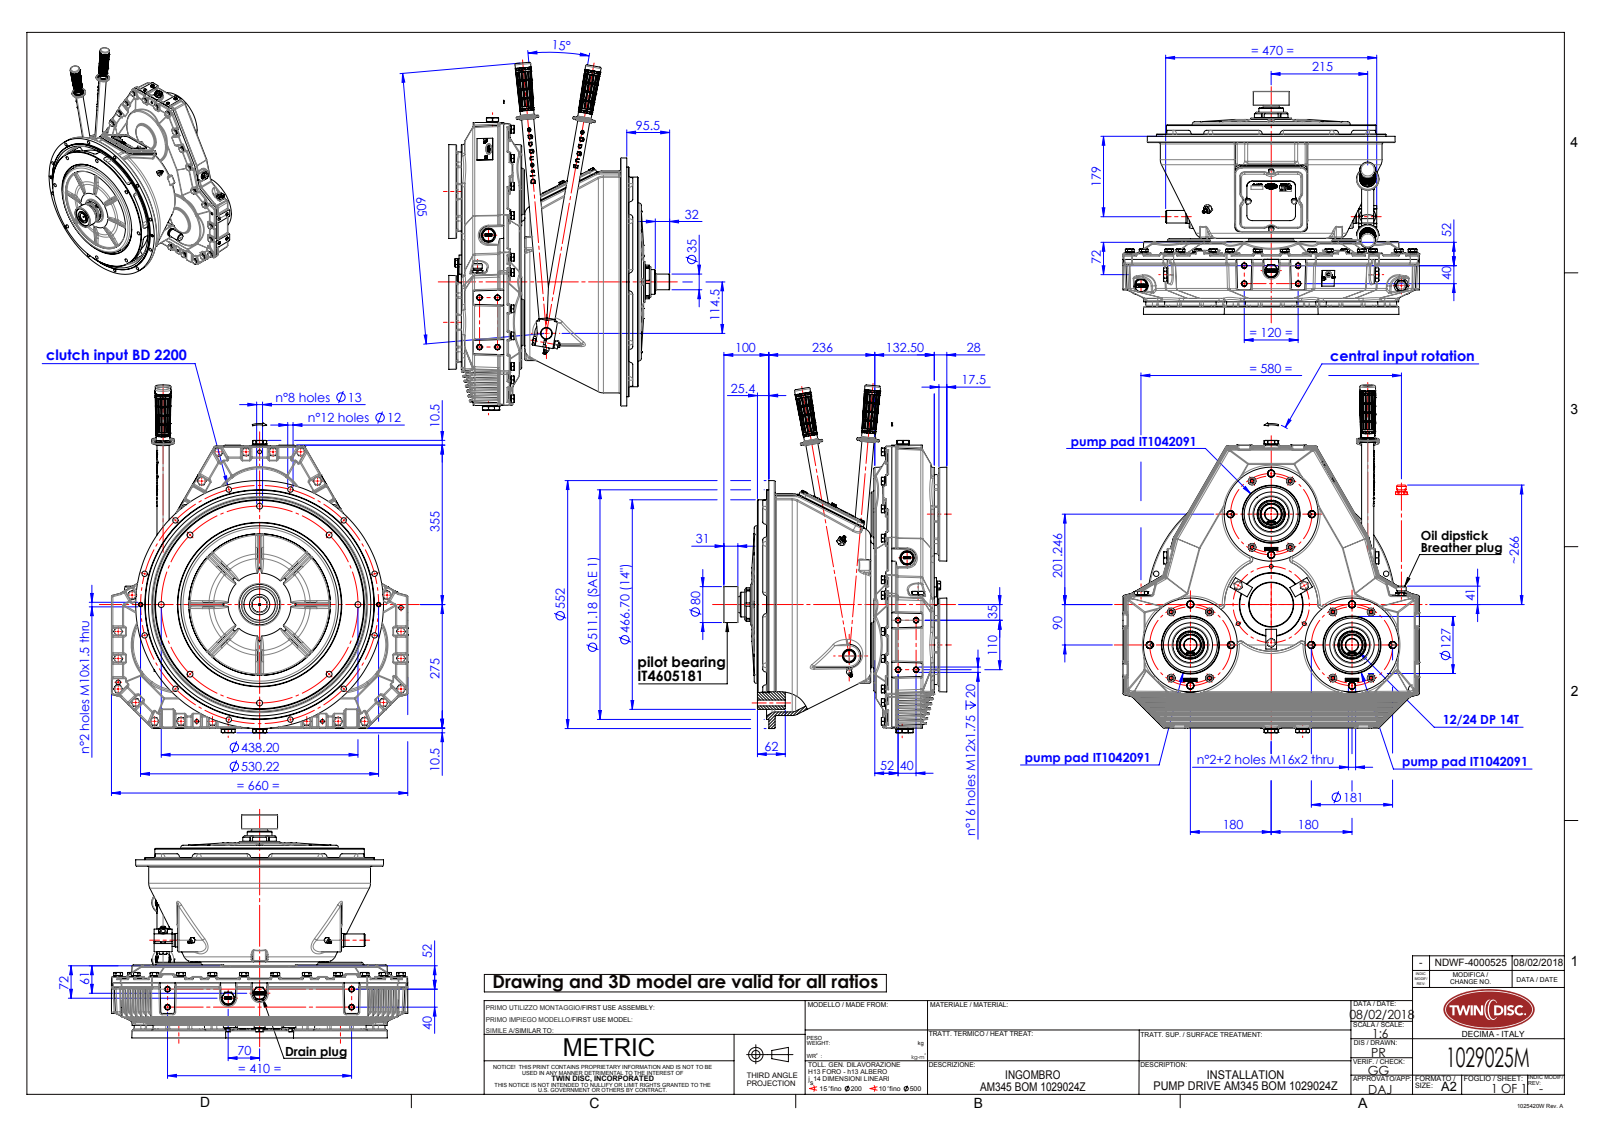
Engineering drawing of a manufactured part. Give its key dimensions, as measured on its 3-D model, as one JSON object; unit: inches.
{"part_name": "ITam230-002_rev00-installation; ITB00610000_rev02-installation; 1029025M; IT4605181-installation (+6 more)", "step_written_by": "SolidWorks 2015 (AUTOMOTIVE_DESIGN)", "units": "inches", "bodies": {"solids": 55, "faces": 11396, "planar": 5451, "cylindrical": 2565, "other": 3380}, "overall_size": [30.491, 25.984, 19.547], "volume_in3": 215.1, "surface_area_in2": 6947, "round_holes": [[0.402, 52], [0.335, 37], [0.413, 32], [0.472, 24], [0.433, 15], [0.512, 14], [0.669, 14], [0.551, 12], [0.63, 12], [0.394, 10], [0.276, 6], [0.197, 5]], "round_bosses_or_shafts": [[0.394, 49], [0.713, 34], [0.638, 34], [0.63, 12], [0.472, 8], [0.709, 6], [0.236, 5], [3.886, 4]], "partial_cylinders_radius": [[0.118, 444], [0.079, 128], [0.197, 98], [0.014, 58], [1.163, 58], [0.059, 44], [0.315, 35], [0.394, 19]], "face_to_face_distances": [1.102, 14.488, 15.591, 5.217, 0.551, 9.409, 0.079, 0.197, 4.803, 15.508], "hole_center_spacings": [3.474, 4.016, 2.26, 4.724, 5.456, 1.575, 8.183, 2.022]}
